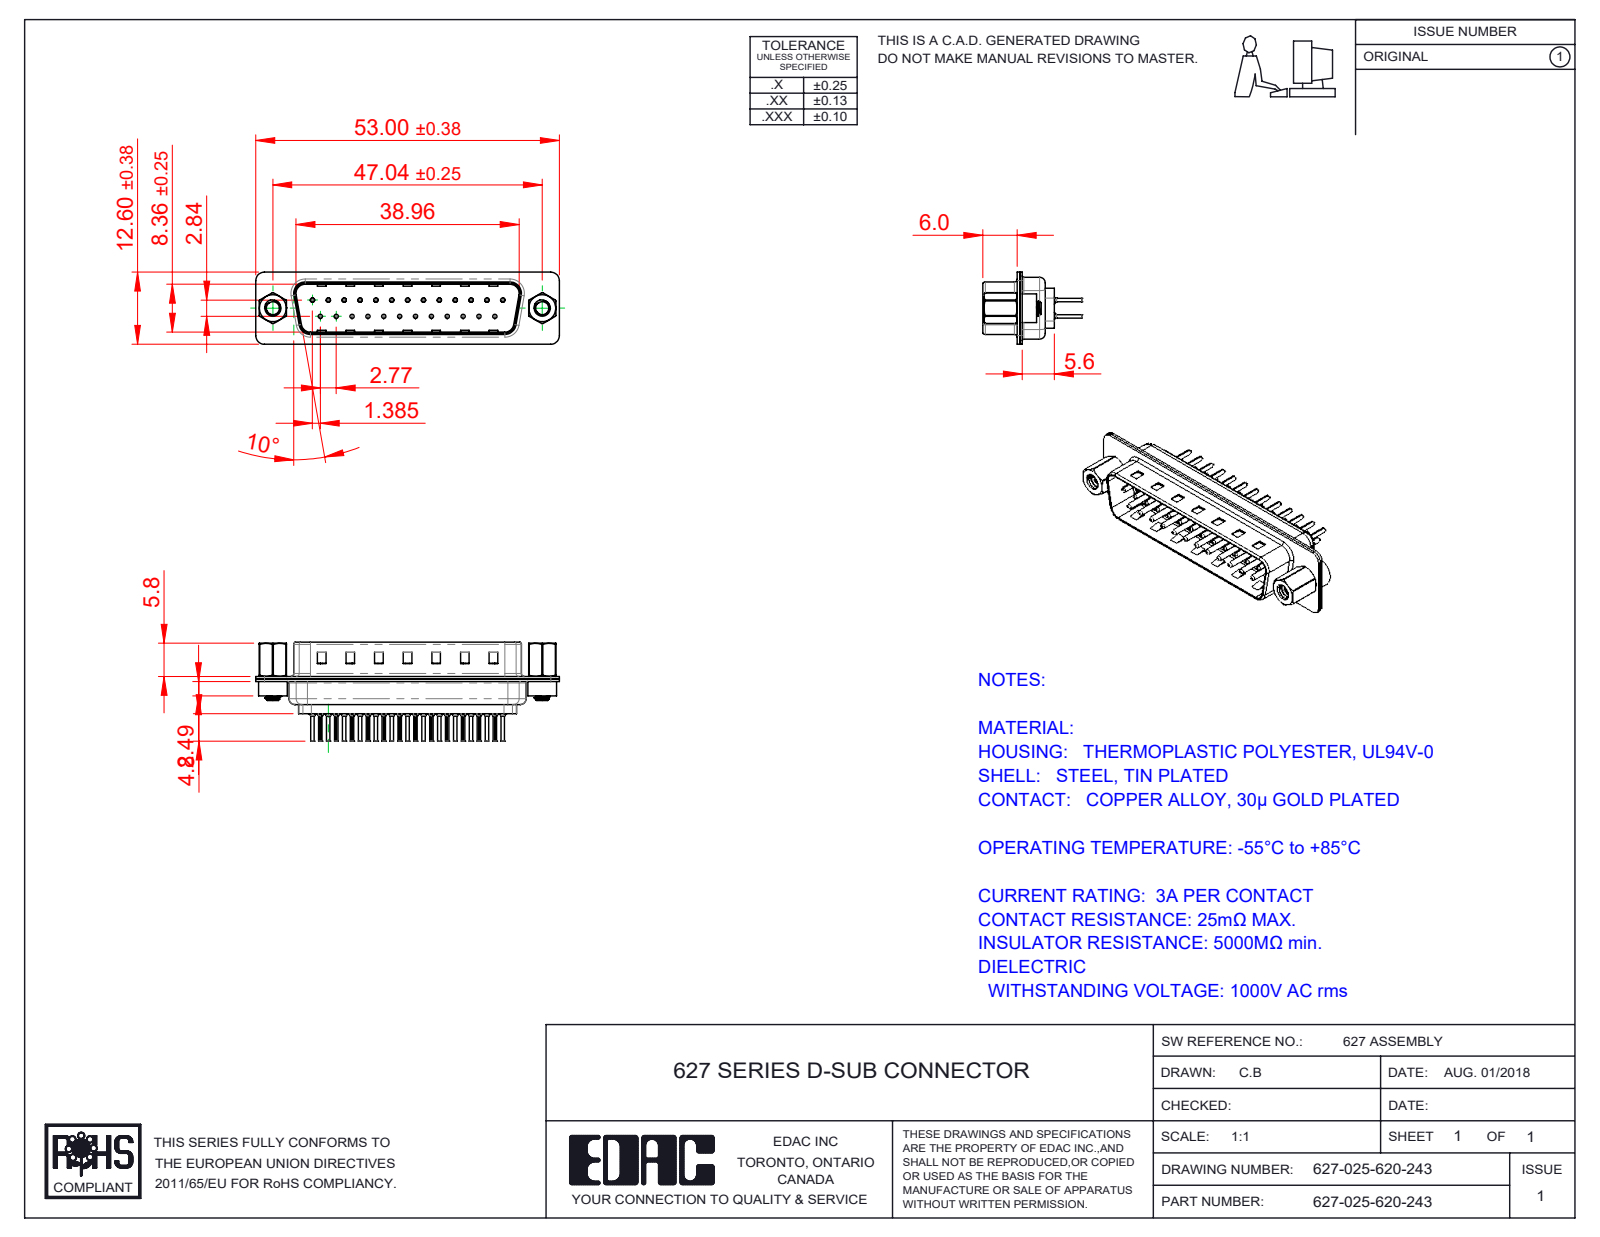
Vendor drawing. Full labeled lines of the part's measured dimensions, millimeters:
Part name (STEP PRODUCT): 627 Housing_25 LP; 627 Shell Rear_25 Contacts; 627-025-620-043; 627 4-40 Hex Standoff (+4 more)
STEP written by: SolidWorks 2020 (CONFIG_CONTROL_DESIGN)
Units: millimetres
Bodies: 32 solids, 2948 faces (793 planar, 1132 cylindrical, 1023 other)
Overall size (bounding box): 53 × 17.3 × 12.6
Volume: 2 890 mm³ · Surface area: 8 277 mm²
Round holes (diameter × count): ⌀0.2 ×25, ⌀0.35 ×25, ⌀1.1 ×25, ⌀1.6 ×25, ⌀2.26 ×2, ⌀2.29 ×2, ⌀4 ×2, ⌀4.8 ×2
Round bosses / shafts (diameter × count): ⌀2 ×25, ⌀1.5 ×25, ⌀0.75 ×25, ⌀0.6 ×25, ⌀5 ×2, ⌀4.9 ×2, ⌀2.79 ×2
Partial cylindrical surfaces — rounded edges, fillets, slot ends (radius × count): R0.1 ×50, R1.5 ×16, R2 ×12, R0.5 ×8, R1.6 ×8, R0.25 ×4, R0.6 ×4, R0.65 ×4
Main face-to-face distances: 0.4, 0.45, 0.82, 9.58, 8.76, 0.9, 1.5, 1.4, 6.5, 6.05
Hole centre spacings: 3.16, 8.31, 2.77, 5.54, 11.08, 16.62, 5.03, 5.04
